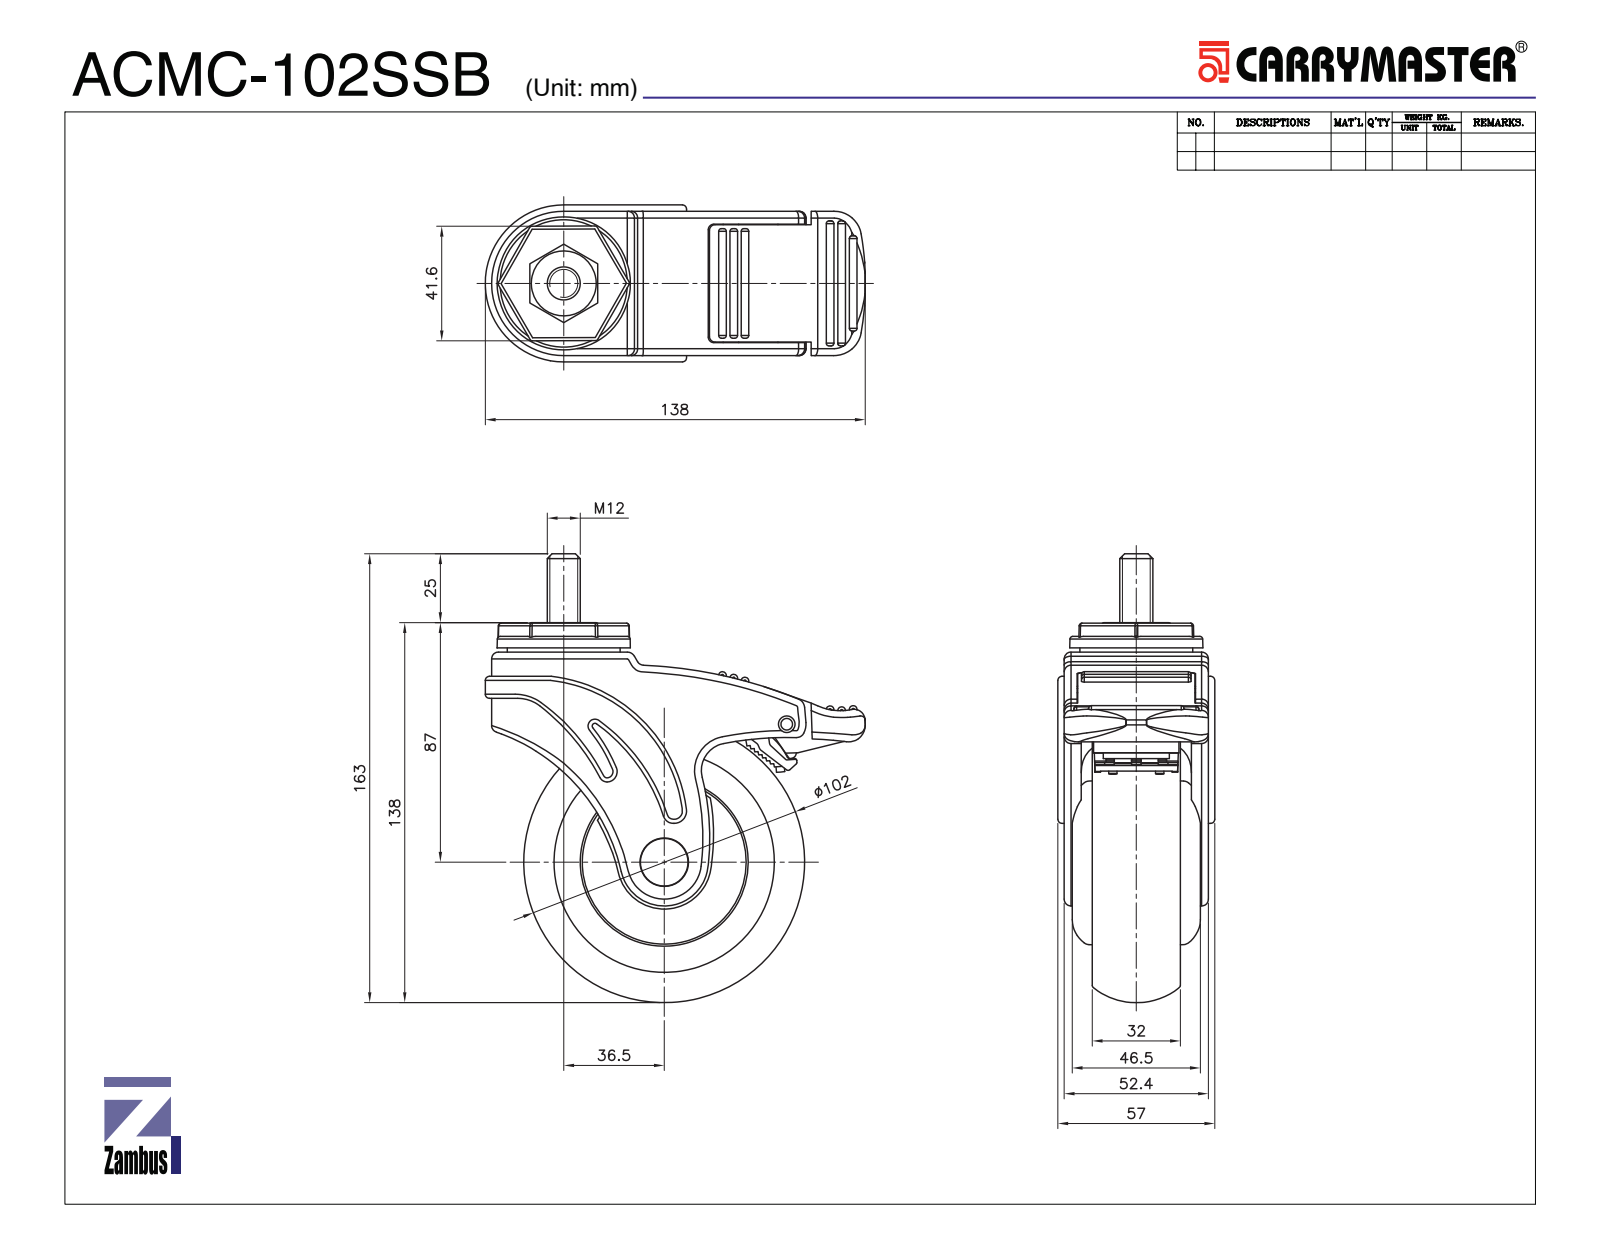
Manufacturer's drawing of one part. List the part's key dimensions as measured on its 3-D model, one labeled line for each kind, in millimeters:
Part name (STEP PRODUCT): ACMC-102 TOP PLATE COVER; ACMC-102 BRAKE; ACMC-102 S TOP PLATE; ACMC-102 WHEEL (+2 more)
STEP written by: SolidWorks 2019 (CONFIG_CONTROL_DESIGN)
Units: millimetres
Bodies: 6 solids, 648 faces (213 planar, 258 cylindrical, 177 other)
Overall size (bounding box): 162.9 × 137.7 × 56.4
Volume: 426 822 mm³ · Surface area: 85 241 mm²
Round holes (diameter × count): ⌀17.3 ×1, ⌀36 ×1, ⌀40.4 ×1, ⌀61 ×1, ⌀80.01 ×1
Round bosses / shafts (diameter × count): ⌀4 ×2, ⌀80 ×1, ⌀60 ×1, ⌀59.5 ×1, ⌀41 ×1, ⌀22 ×1, ⌀17 ×1, ⌀10.25 ×1
Partial cylindrical surfaces — rounded edges, fillets, slot ends (radius × count): R0.5 ×27, R1 ×16, R2.5 ×7, R1.4 ×6, R2 ×6, R1.5 ×4, R3 ×3, R10 ×3
Main face-to-face distances: 4.2, 36.2, 6, 42.2, 10.2, 46.4, 40.4, 32, 52.4, 6.25
